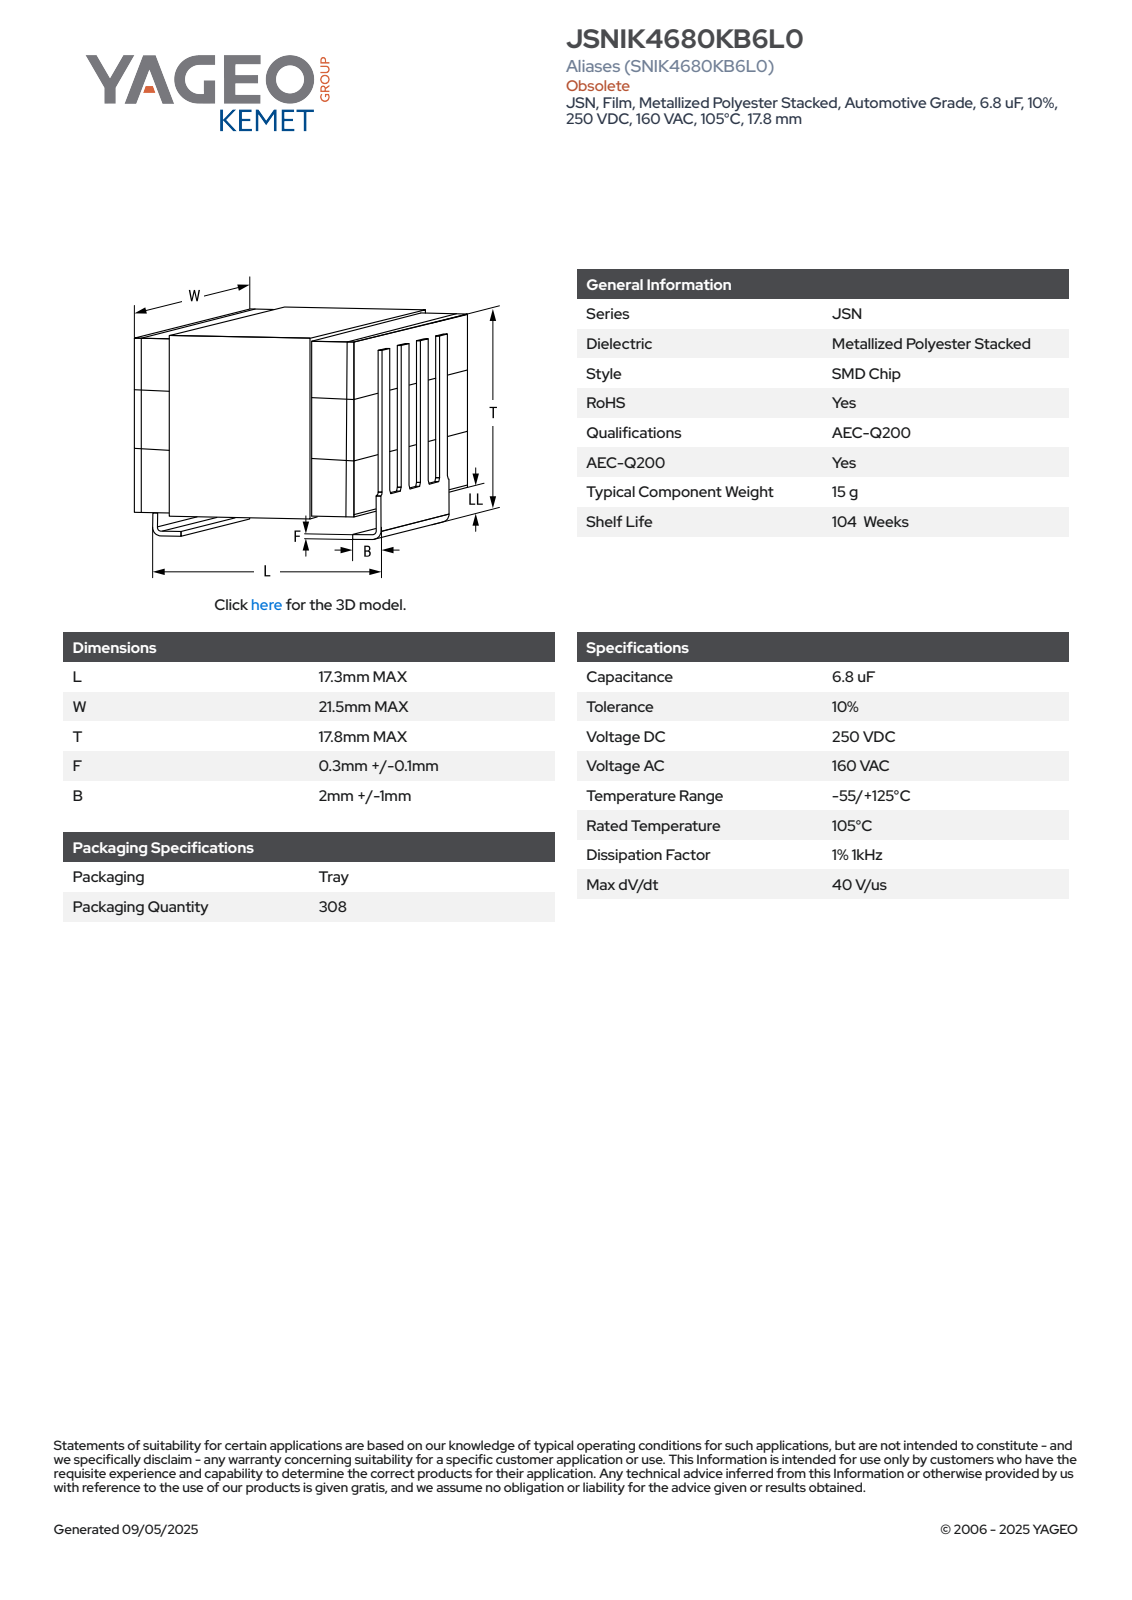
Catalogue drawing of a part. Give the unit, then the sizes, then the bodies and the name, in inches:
Units: inches
Overall size (bounding box): 0.846 × 0.701 × 0.681
Partial cylindrical surfaces — rounded edges, fillets, slot ends (radius × count): R0.008 ×4
Main face-to-face distances: 0.192, 0.387, 0.016, 0.194, 0.383, 0.188, 0.665, 0.681, 0.196, 0.391
Volume: 0.326 in³ · Surface area: 4.783 in²
Bodies: 4 solids, 101 faces (97 planar, 4 cylindrical, 0 other)
Part name (STEP PRODUCT): CFS_KJSN_L17.3W21.5T17.8F0.40
STEP written by: SolidWorks 2014 (AUTOMOTIVE_DESIGN)
